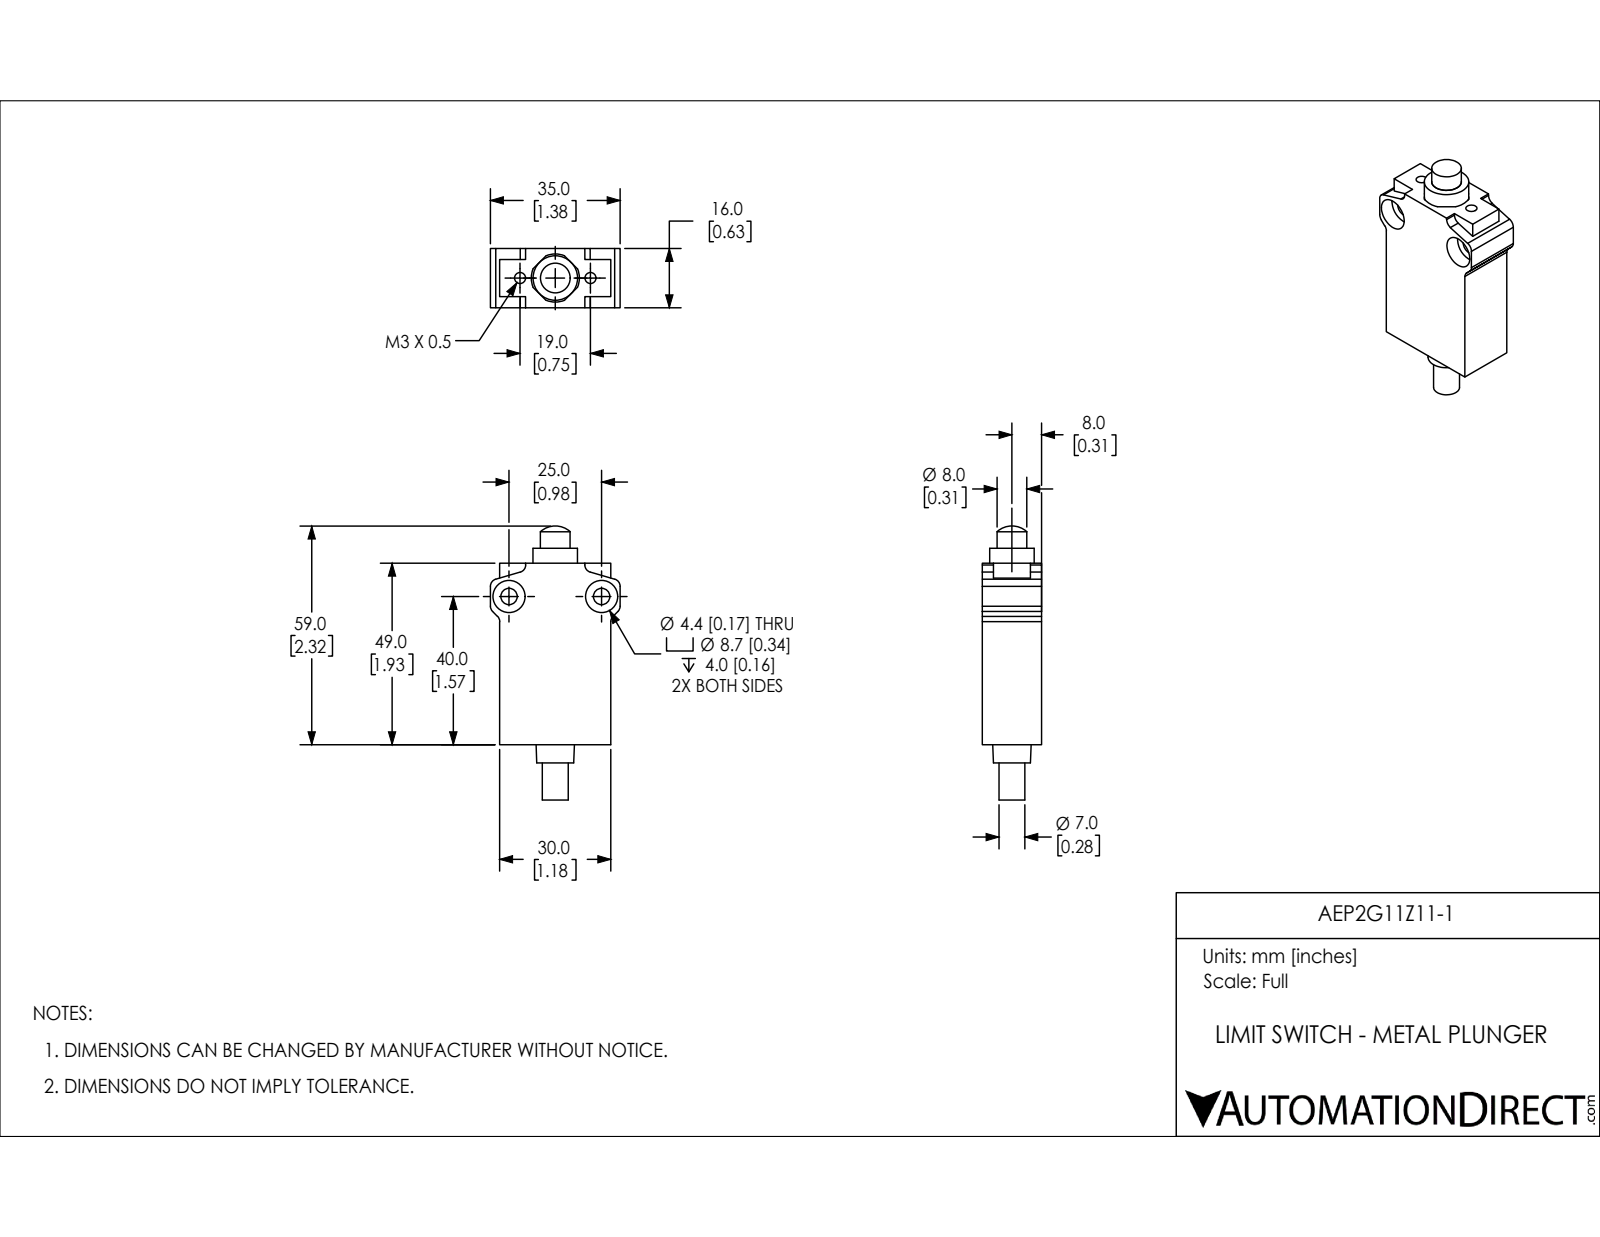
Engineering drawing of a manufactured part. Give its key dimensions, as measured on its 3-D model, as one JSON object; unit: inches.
{"part_name": "AEP2G11Z11-1", "step_written_by": "SolidWorks 2018 (AUTOMOTIVE_DESIGN)", "units": "inches", "bodies": {"solids": 3, "faces": 93, "planar": 38, "cylindrical": 52, "other": 3}, "overall_size": [2.909, 1.378, 0.63], "volume_in3": 1.436, "surface_area_in2": 11.6, "round_holes": [[0.118, 2], [0.173, 2], [0.343, 2], [0.315, 1]], "round_bosses_or_shafts": [[0.472, 1], [0.276, 1]], "partial_cylinders_radius": [[0.079, 8], [0.256, 1]], "face_to_face_distances": [0.63, 1.181, 0.157, 1.929, 0.472, 0.098, 1.28, 0.039, 1.74, 0.189], "hole_center_spacings": [0.374, 0.748, 0.984]}
